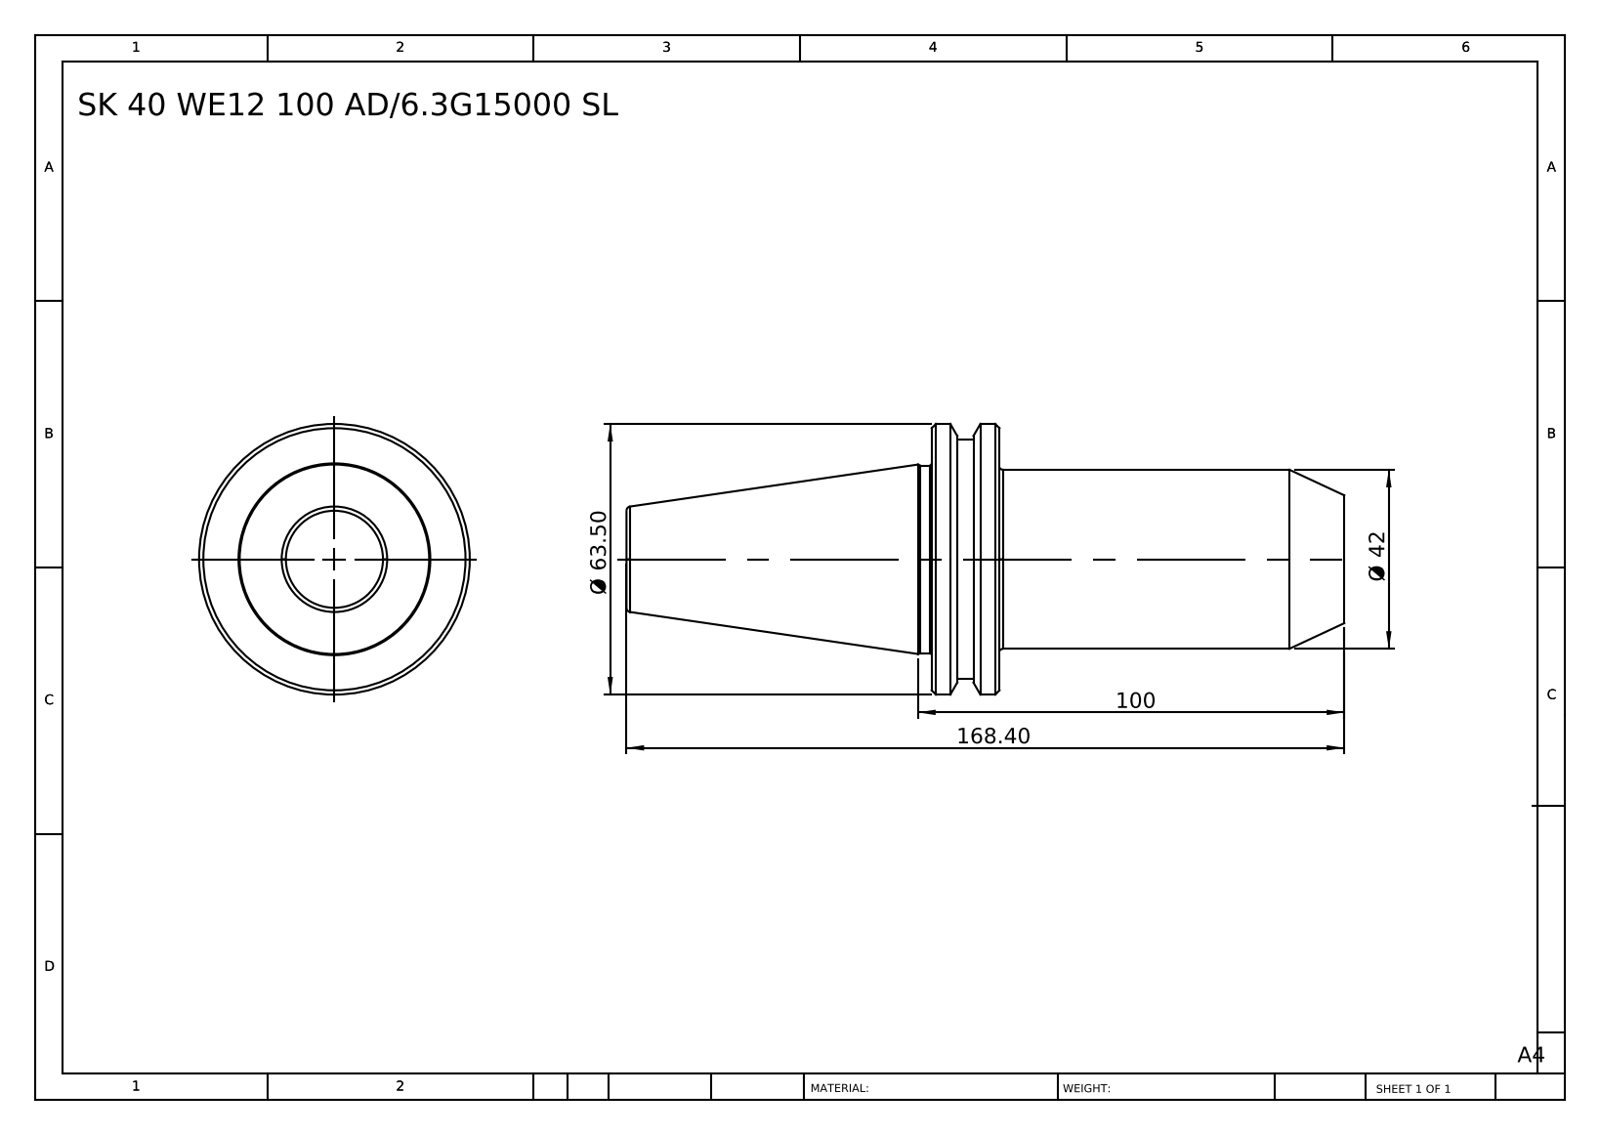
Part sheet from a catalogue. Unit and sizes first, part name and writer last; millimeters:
Units: millimetres
Overall size (bounding box): 168.4 × 63.5 × 63.5
Round bosses / shafts (diameter × count): ⌀63.5 ×1, ⌀56 ×1, ⌀44 ×1, ⌀42 ×1
Main face-to-face distances: 15.9, 80.9, 96.8, 168.4, 87.5, 71.6, 90.8, 9.9, 6, 77.6
Volume: 224 591 mm³ · Surface area: 26 800 mm²
Bodies: 1 solid, 36 faces (6 planar, 10 cylindrical, 20 other)
Part name (STEP PRODUCT): SK40 WE12 100 AD-6.3G15000 SL
STEP written by: SolidWorks 2014 (CONFIG_CONTROL_DESIGN)
